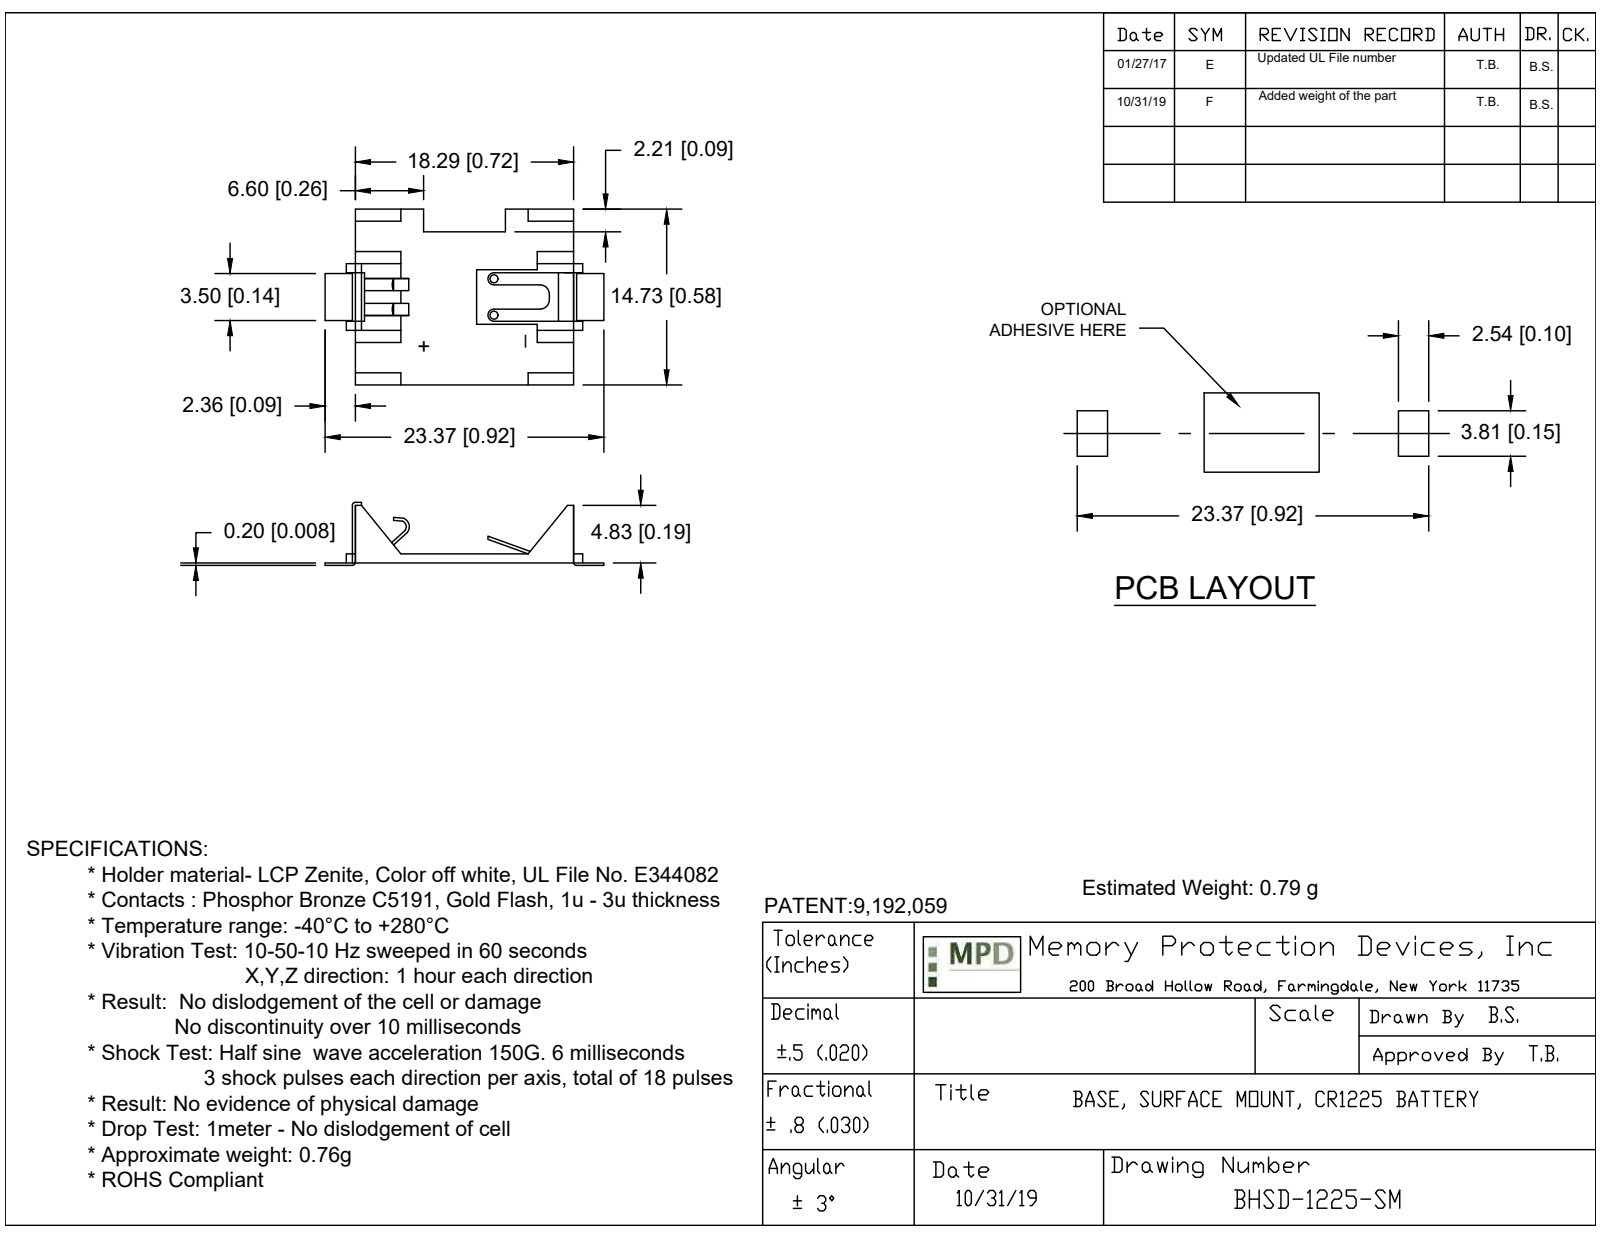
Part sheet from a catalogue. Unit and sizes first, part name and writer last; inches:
Units: inches
Overall size (bounding box): 0.92 × 0.58 × 0.198
Partial cylindrical surfaces — rounded edges, fillets, slot ends (radius × count): R0.012 ×8, R0.004 ×7, R0.02 ×5, R0.016 ×4, R0.008 ×2, R0.007 ×1, R0.015 ×1
Main face-to-face distances: 0.03, 0.065, 0.655, 0.72, 0.022, 0.154, 0.426, 0.19, 0.161, 0.591
Volume: 0.022 in³ · Surface area: 1.731 in²
Bodies: 3 solids, 188 faces (150 planar, 38 cylindrical, 0 other)
Part name (STEP PRODUCT): BHSD-1225-SM
STEP written by: SolidWorks 2021 (AUTOMOTIVE_DESIGN)
